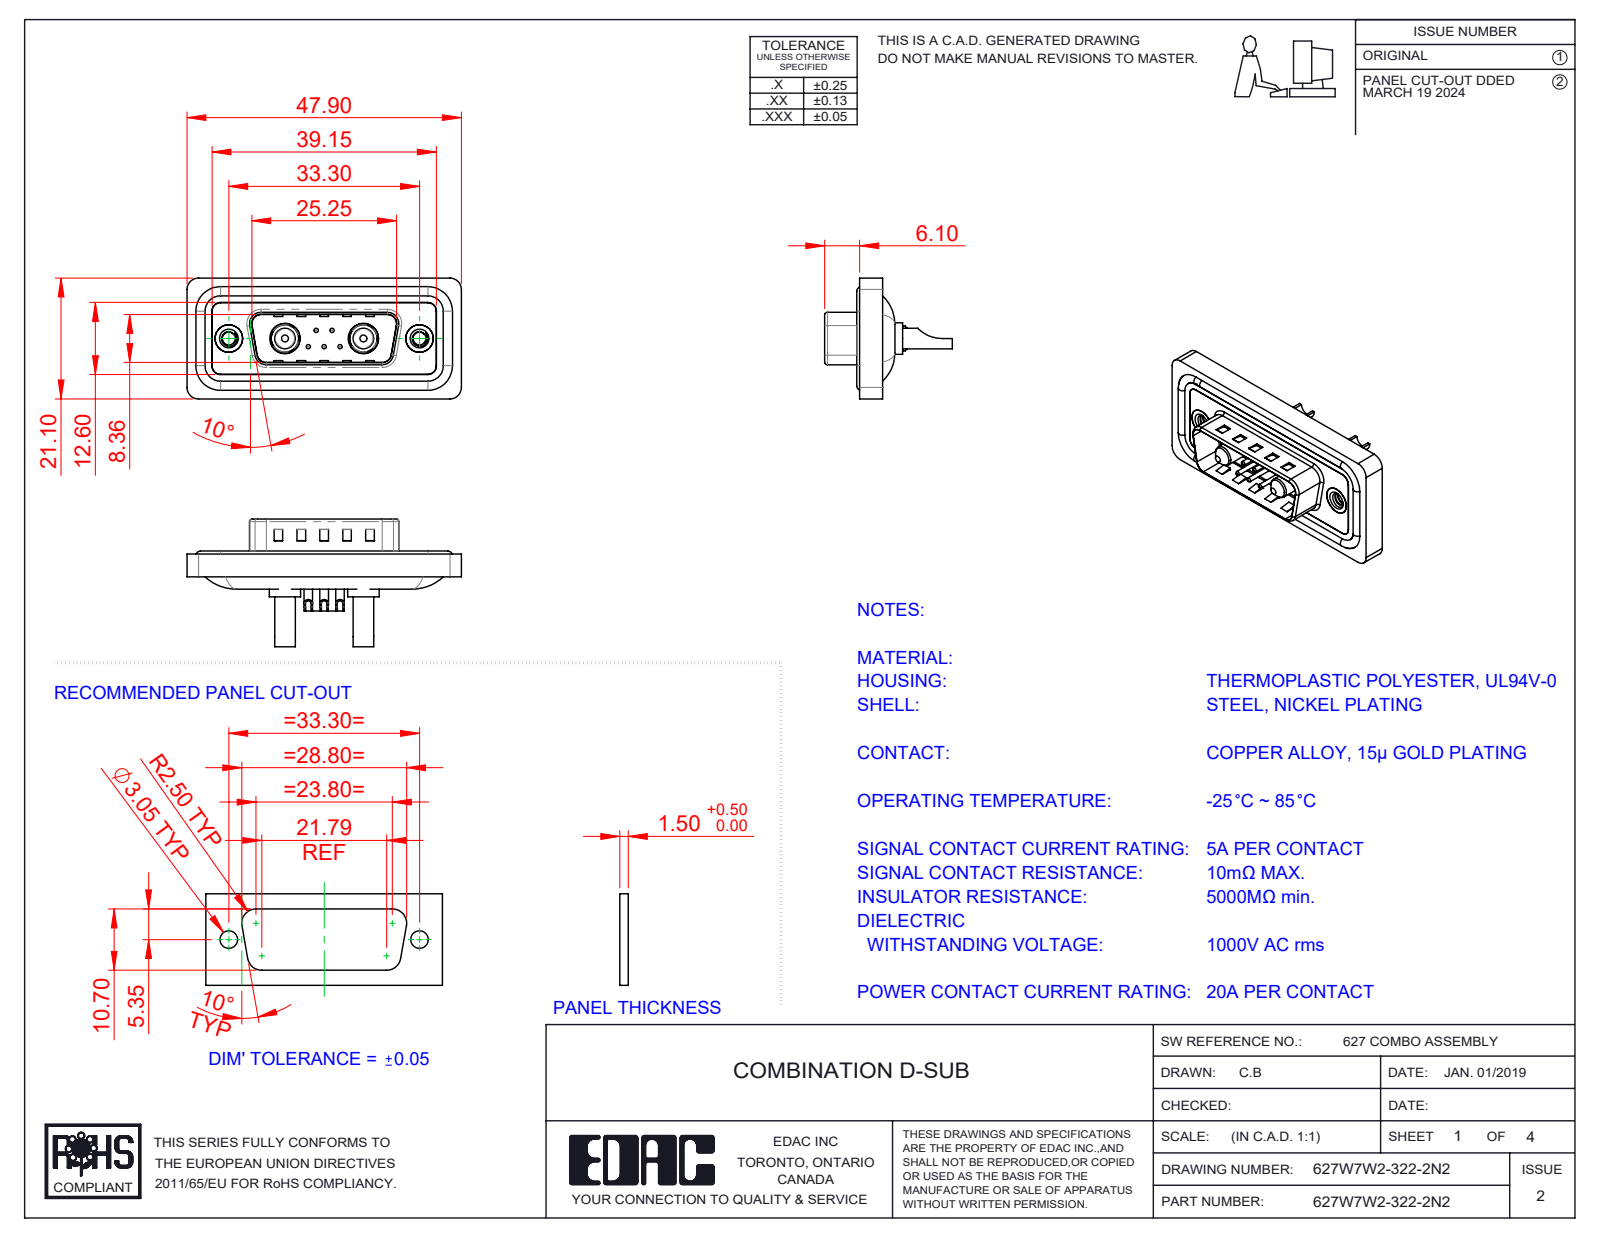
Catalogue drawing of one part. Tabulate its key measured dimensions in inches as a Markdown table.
| quantity | value |
| --- | --- |
| part name | 627Combo Threaded Rivet_2; 627Combo Shell Rear_15 Contacts; 627W7W2-322-2N2; 627Combo Contact Row 1_22 (+5 more) |
| STEP written by | SolidWorks 2023 (CONFIG_CONTROL_DESIGN) |
| units | inches |
| bodies | 16 solids, 724 faces (248 planar, 308 cylindrical, 168 other) |
| overall size | 1.886 × 0.878 × 0.831 |
| volume | 0.339 in³ |
| surface area | 13.95 in² |
| round holes (diameter × count) | 0.03 × 5, 0.039 × 5, 0.063 × 5, 0.079 × 5, 0.089 × 2, 0.106 × 2, 0.157 × 2, 0.189 × 2, 0.191 × 2, 0.197 × 2, 0.209 × 2 |
| round bosses / shafts (diameter × count) | 0.059 × 5, 0.063 × 4, 0.217 × 2, 0.205 × 2, 0.193 × 2, 0.187 × 2, 0.148 × 2, 0.142 × 2 |
| partial cylindrical surfaces (radius × count) | 0.059 × 26, 0.079 × 20, 0.02 × 8, 0.063 × 8, 0.039 × 6, 0.01 × 4, 0.024 × 4, 0.026 × 4 |
| main face-to-face distances | 0.016, 0.043, 0.063, 0.059, 0.02, 0.122, 0.114, 0.032, 0.377, 0.098 |
| hole center spacings | 0.124, 0.109, 0.386, 0.925, 0.17, 0.17, 0.198, 0.198 |
